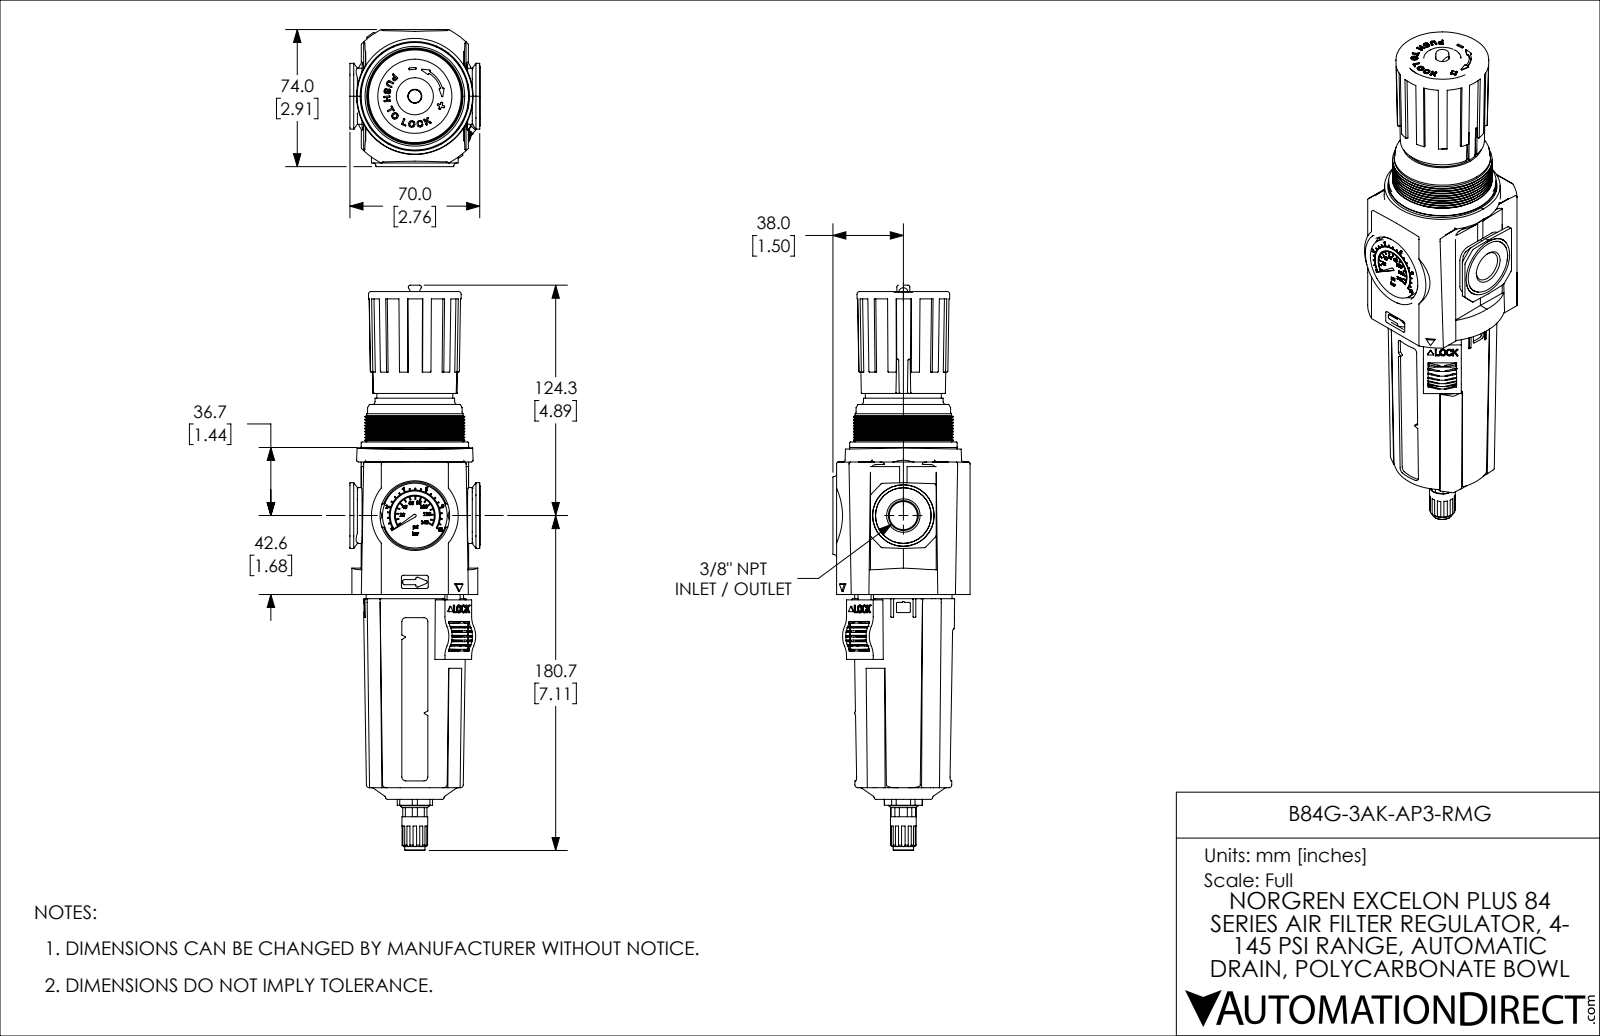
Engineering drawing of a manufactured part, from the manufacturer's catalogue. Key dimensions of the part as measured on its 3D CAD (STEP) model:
Part name (STEP PRODUCT): B84G-3AK-AP3-RMG
STEP written by: SolidWorks 2021 (CONFIG_CONTROL_DESIGN)
Units: inches
Bodies: 8 solids, 2561 faces (955 planar, 1193 cylindrical, 413 other)
Overall size (bounding box): 12.005 × 2.913 × 2.766
Volume: 46.16 in³ · Surface area: 207 in²
Round holes (diameter × count): ⌀0.177 ×2, ⌀0.059 ×1, ⌀0.197 ×1, ⌀0.22 ×1, ⌀0.246 ×1, ⌀0.776 ×1, ⌀0.969 ×1, ⌀1.319 ×1, ⌀2.323 ×1, ⌀2.461 ×1
Round bosses / shafts (diameter × count): ⌀0.299 ×2, ⌀0.157 ×2, ⌀2.283 ×1, ⌀2.119 ×1, ⌀2.047 ×1, ⌀2.026 ×1, ⌀2.008 ×1, ⌀1.693 ×1
Partial cylindrical surfaces — rounded edges, fillets, slot ends (radius × count): R0.039 ×34, R0.012 ×27, R0.02 ×26, R0.01 ×24, R0.047 ×18, R0.028 ×16, R0.03 ×16, R0.004 ×14
Main face-to-face distances: 2.719, 2.323, 0.035, 2.683, 0.512, 0.622, 2.096, 2.061, 3.866, 3.831
Hole centre spacings: 0.856, 1.713
